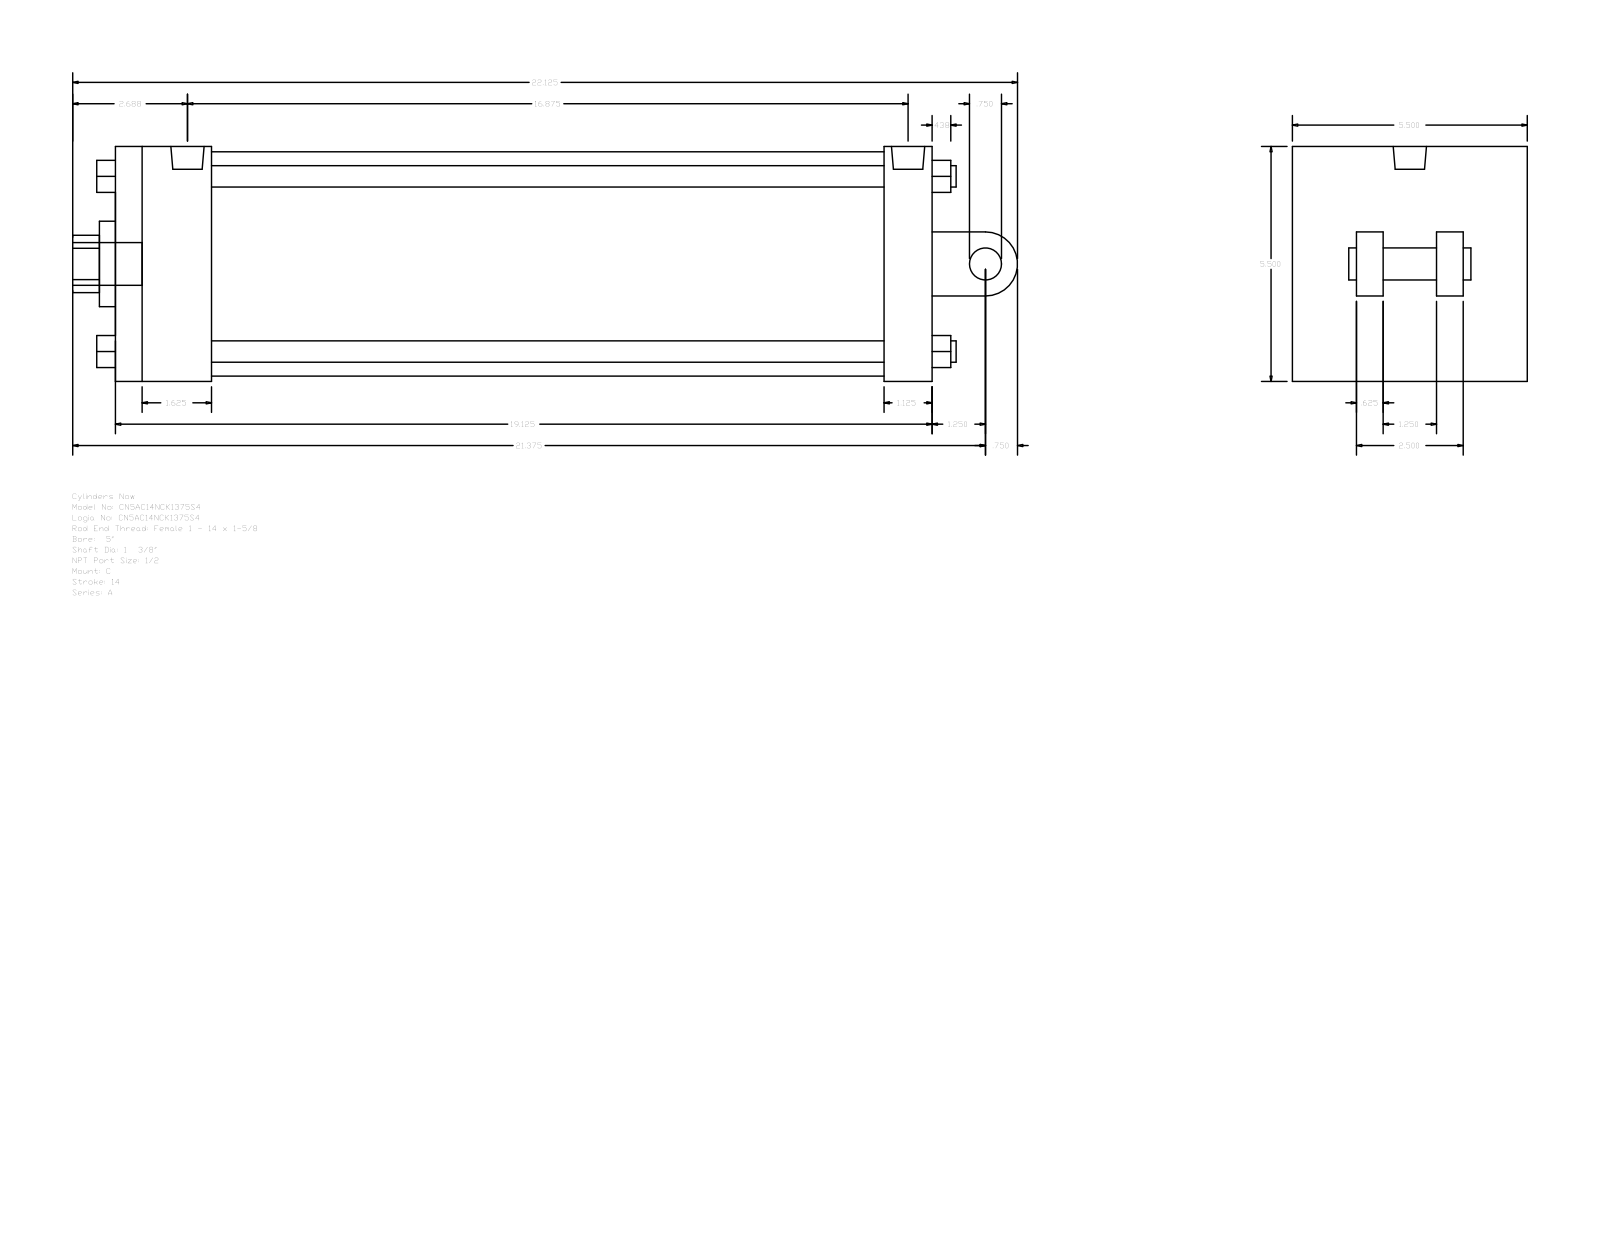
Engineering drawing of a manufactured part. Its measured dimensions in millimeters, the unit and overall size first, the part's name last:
Units: millimetres
Overall size (bounding box): 561.98 × 139.7 × 139.7
Round holes (diameter × count): ⌀8.73 ×2, ⌀19.77 ×1, ⌀34.92 ×1, ⌀50.8 ×1, ⌀133.35 ×1
Round bosses / shafts (diameter × count): ⌀12.7 ×4, ⌀8.73 ×2, ⌀25.4 ×1, ⌀19.77 ×1, ⌀19.05 ×1
Partial cylindrical surfaces — rounded edges, fillets, slot ends (radius × count): R17.06 ×1, R19.05 ×1
Main face-to-face distances: 139.7, 485.78, 28.58, 57.15, 457.2, 400.05, 428.63, 38.1, 15.87, 53.97
Hole centre spacings: 2.39
Bodies: 0 solids, 135 faces (102 planar, 33 cylindrical, 0 other)
Part name (STEP PRODUCT): A_C__0500_1.375
STEP written by: GSSL Pune (CONFIG_CONTROL_DESIGN)
